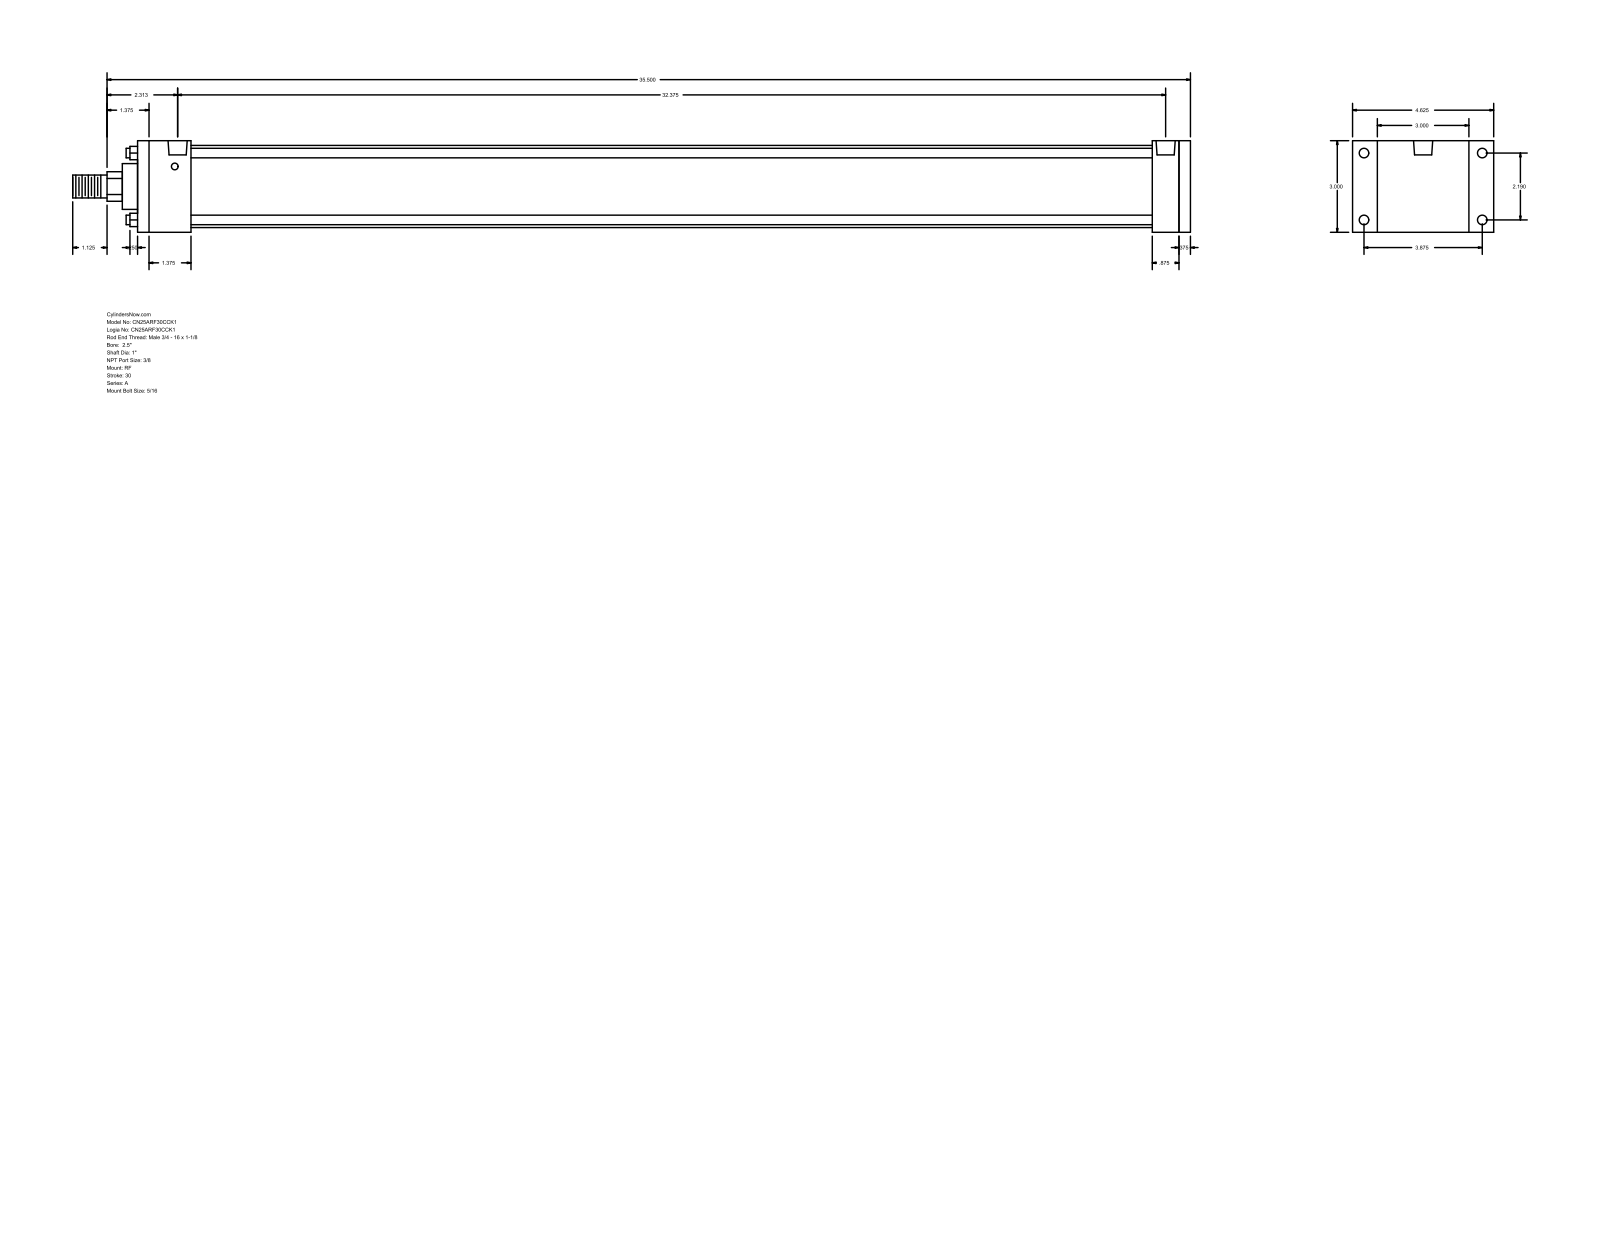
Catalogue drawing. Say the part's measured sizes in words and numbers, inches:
The part is named "A_RF__0250_1". Its 3-D file was written by "GSSL Pune (CONFIG_CONTROL_DESIGN)". It is 0 solids with 92 faces: 64 planar, 28 cylindrical and 0 other. Overall it measures 36.625 by 4.625 by 3 inches. Round holes: 4 of diameter 0.219, 4 of diameter 0.313, 2 of diameter 0.627. Round bosses or shafts: 4 of diameter 0.313, 1 of diameter 2.69, 1 of diameter 1.5, 1 of diameter 1, 1 of diameter 0.75. Partial cylindrical surfaces (rounded edges, fillets, slot ends): 1 of radius 0.484. The main face-to-face distances are 3, 34.5, 0.375, 34.125, 1.75, 33.25, 31.5, 32.375, 32.75, 0.875. The hole center spacings are 0.094, 2.19, 3.875, 4.451, 32.469, 32.562, 32.375.
